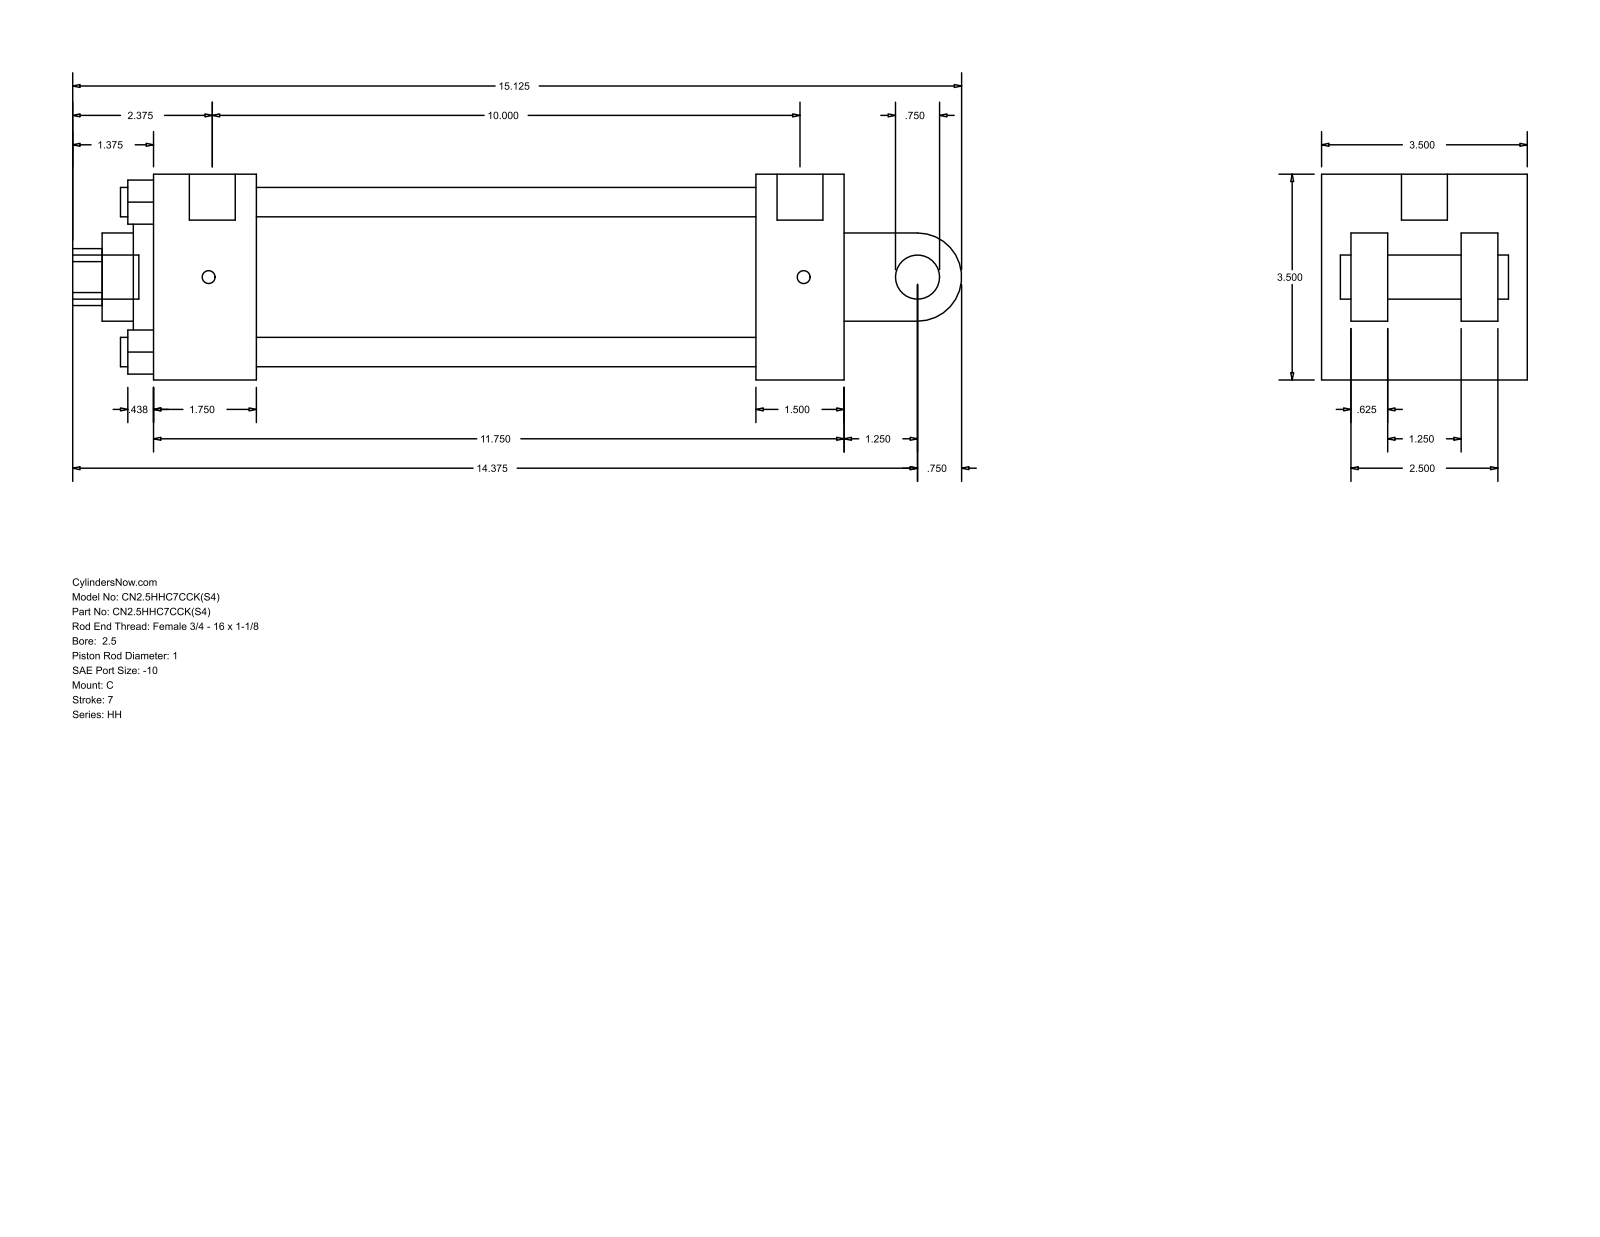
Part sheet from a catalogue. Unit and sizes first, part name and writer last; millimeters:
Units: millimetres
Overall size (bounding box): 384.18 × 88.9 × 88.9
Round holes (diameter × count): ⌀12.7 ×4, ⌀5.56 ×2, ⌀19.84 ×1, ⌀25.4 ×1, ⌀38.1 ×1, ⌀60.33 ×1, ⌀73.03 ×1
Round bosses / shafts (diameter × count): ⌀19.05 ×2, ⌀5.56 ×2, ⌀19.84 ×1
Partial cylindrical surfaces — rounded edges, fillets, slot ends (radius × count): R12.29 ×1, R19.05 ×1
Main face-to-face distances: 88.9, 298.46, 63.5, 15.87, 260.35, 38.11, 44.46, 215.89, 254, 12.7
Hole centre spacings: 45.79, 64.76, 91.58, 1.59
Bodies: 0 solids, 101 faces (71 planar, 30 cylindrical, 0 other)
Part name (STEP PRODUCT): HH_C__0250_1
STEP written by: GSSL Pune (CONFIG_CONTROL_DESIGN)
